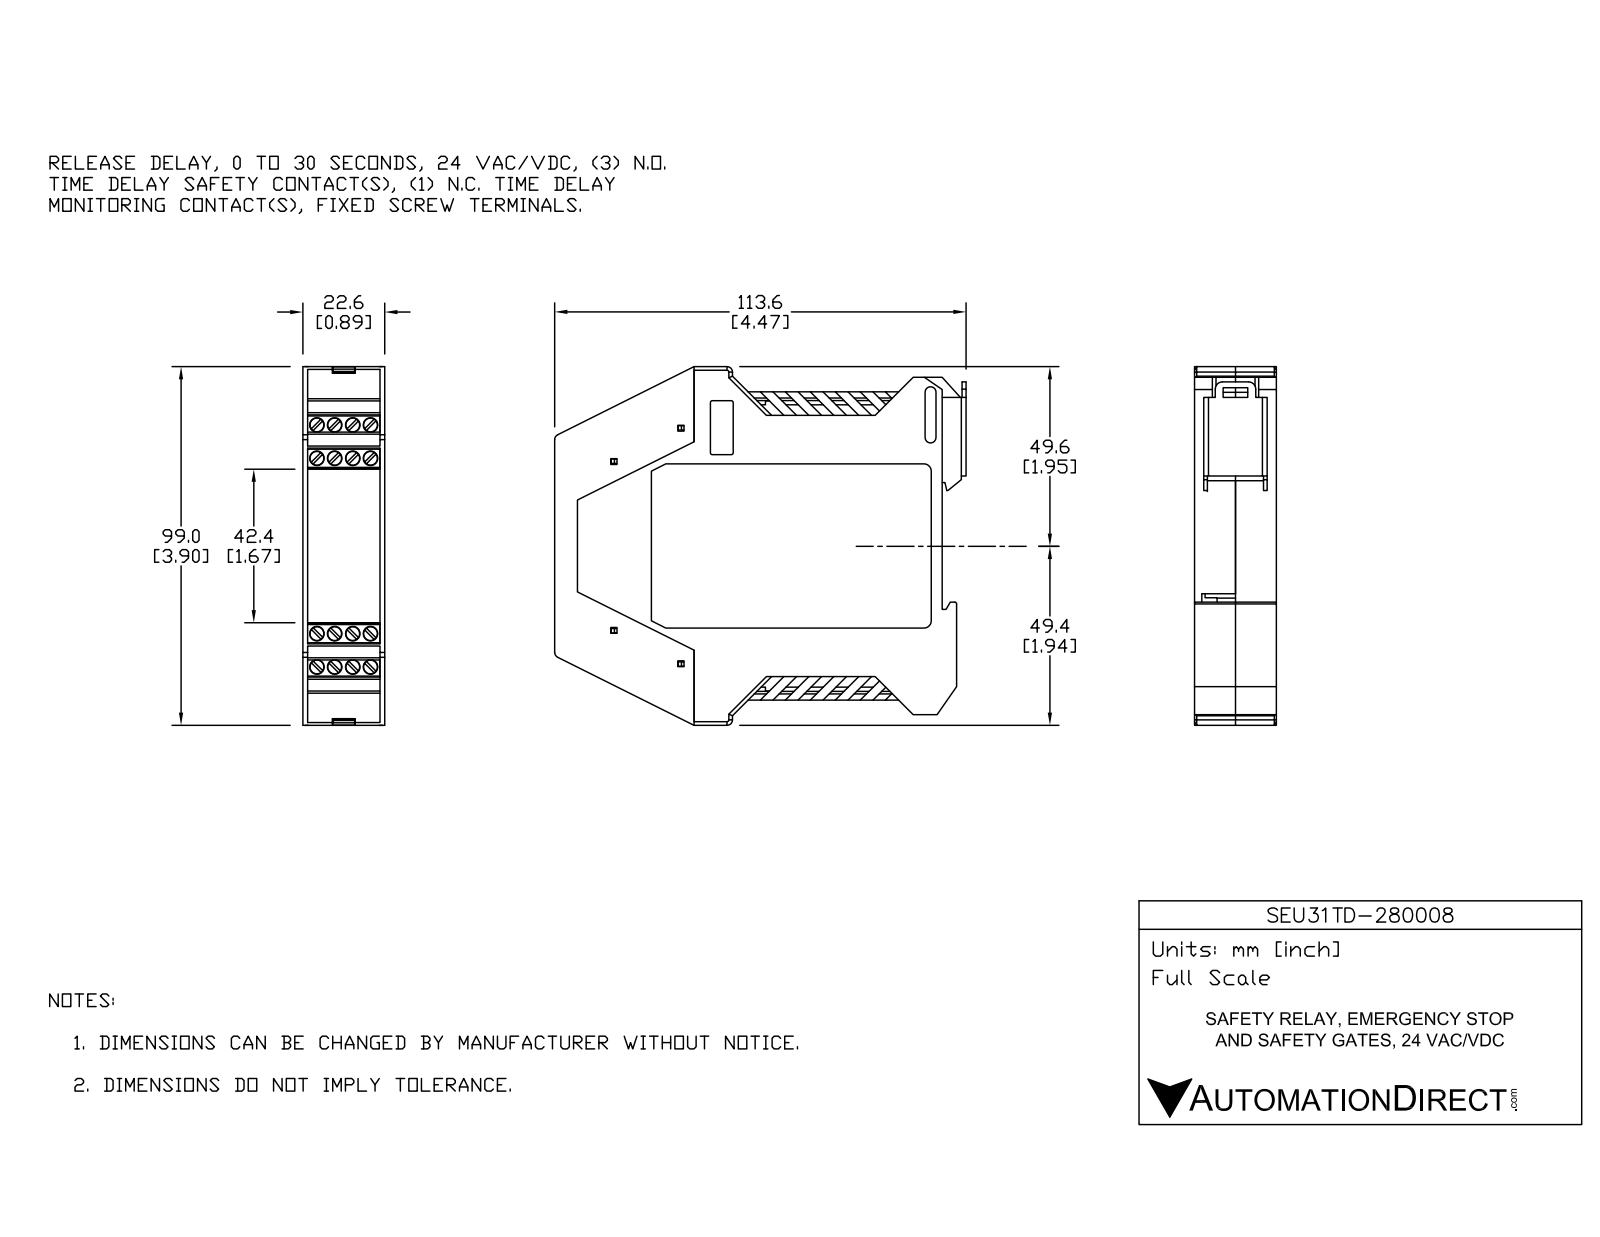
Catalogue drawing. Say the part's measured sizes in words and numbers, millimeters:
The part is named "280-Viper-22 (STEP format)". Its 3-D file was written by "SolidWorks 2015 (CONFIG_CONTROL_DESIGN)". It is 10 solids with 1899 faces: 1607 planar, 280 cylindrical and 12 other. Overall it measures 113.6 by 99 by 22.6 millimeters. Its volume is 64 707 cubic millimeters and its surface area 69 278 square millimeters. Round holes: 16 of diameter 4, 2 of diameter 2. Round bosses or shafts: 16 of diameter 3.8, 16 of diameter 1.4, 2 of diameter 1.9. Partial cylindrical surfaces (rounded edges, fillets, slot ends): 39 of radius 0.5, 24 of radius 0.3, 18 of radius 0.2, 6 of radius 1.5, 4 of radius 0.65, 4 of radius 0.8, 4 of radius 2, 2 of radius 1.3. The main face-to-face distances are 21.1, 1.3, 1.5, 20.9, 22.4, 19.6, 22.6, 1.1, 11.3, 11.1. The hole center spacings are 4.9, 9.2, 9.9, 10.42, 13.51, 57.6, 57.81, 58.44.
